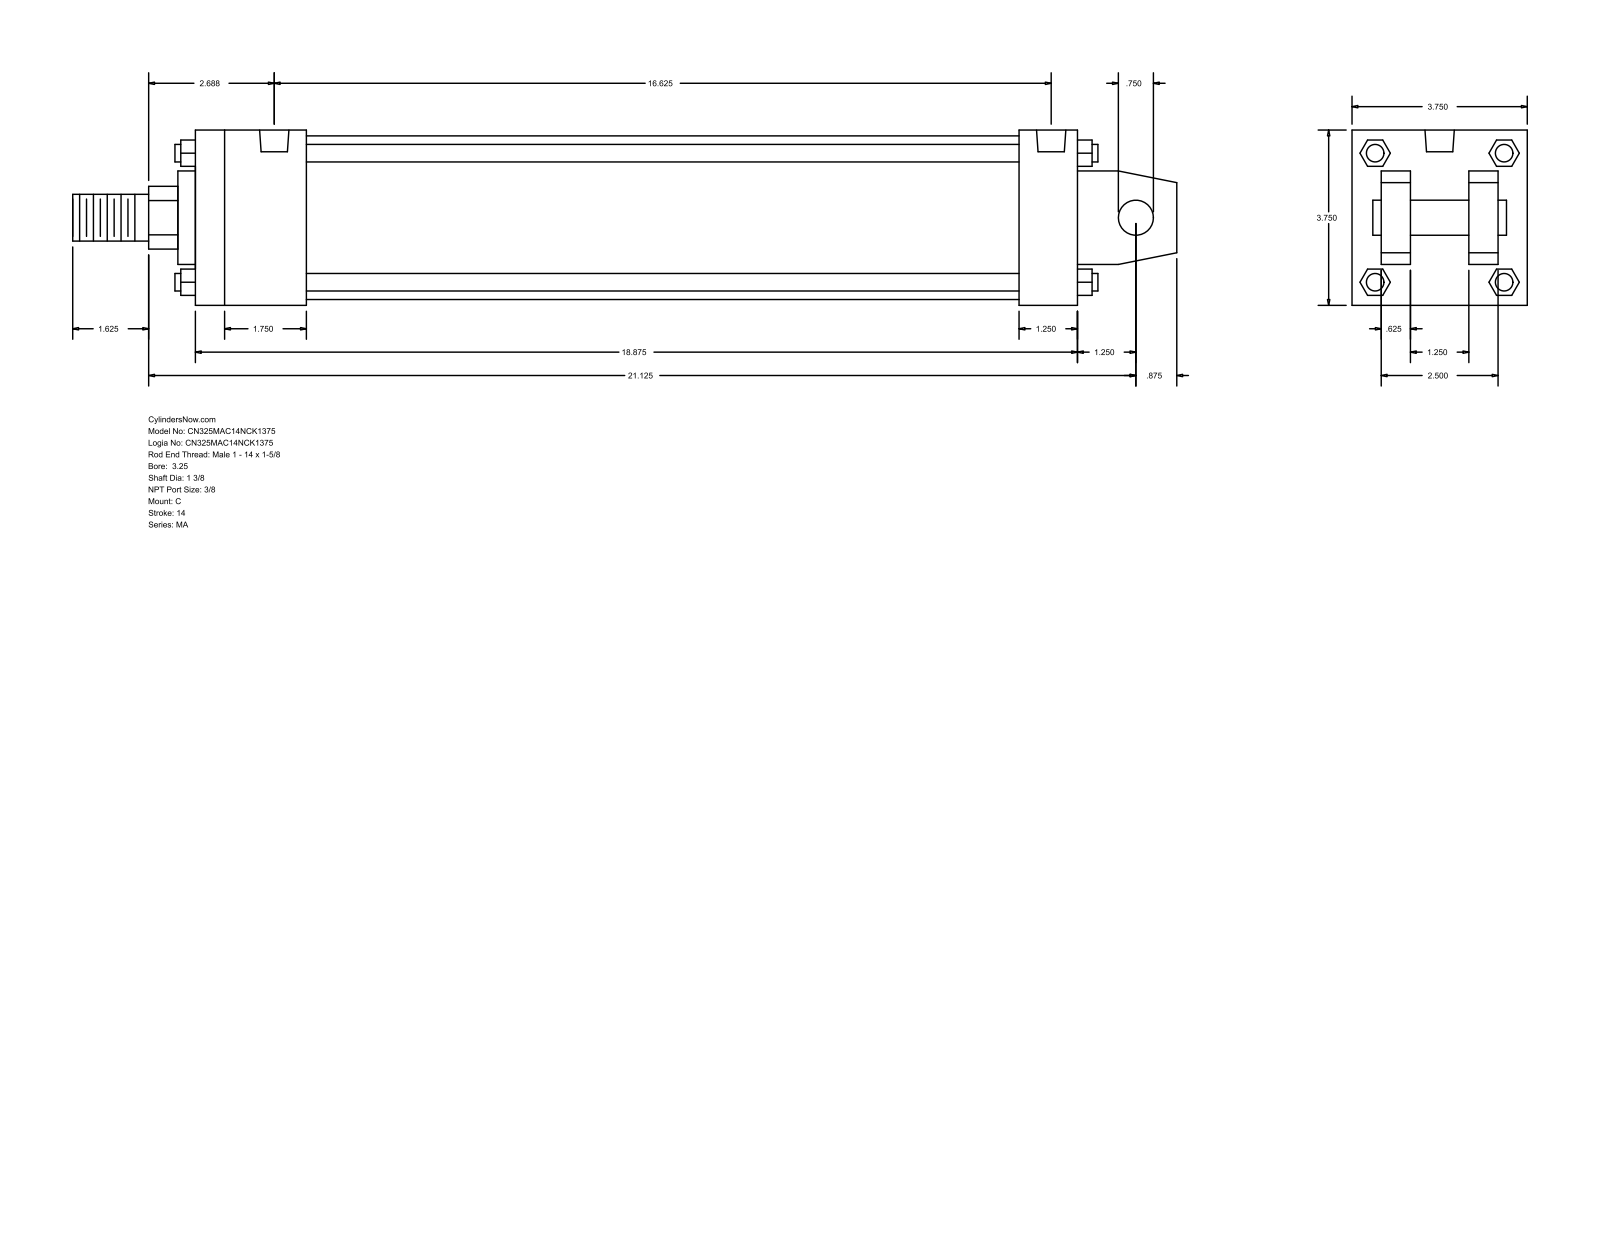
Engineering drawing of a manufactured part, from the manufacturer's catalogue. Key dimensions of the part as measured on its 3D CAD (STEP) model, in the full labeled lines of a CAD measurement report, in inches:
Part name (STEP PRODUCT): MA_C__0325_1.375
STEP written by: GSSL Pune (CONFIG_CONTROL_DESIGN)
Units: inches
Bodies: 0 solids, 139 faces (108 planar, 31 cylindrical, 0 other)
Overall size (bounding box): 23.625 × 3.75 × 3.75
Round holes (diameter × count): ⌀0.437 ×4, ⌀0.627 ×2
Round bosses / shafts (diameter × count): ⌀0.375 ×4, ⌀3.5 ×1, ⌀2 ×1, ⌀1.375 ×1, ⌀1 ×1, ⌀0.75 ×1
Partial cylindrical surfaces — rounded edges, fillets, slot ends (radius × count): R0.672 ×1
Main face-to-face distances: 3.75, 0.625, 2.5, 18.875, 1.25, 3.125, 1.875, 17.625, 1.25, 2.375
Hole centre spacings: 0.188, 16.25, 16.437, 16.625
